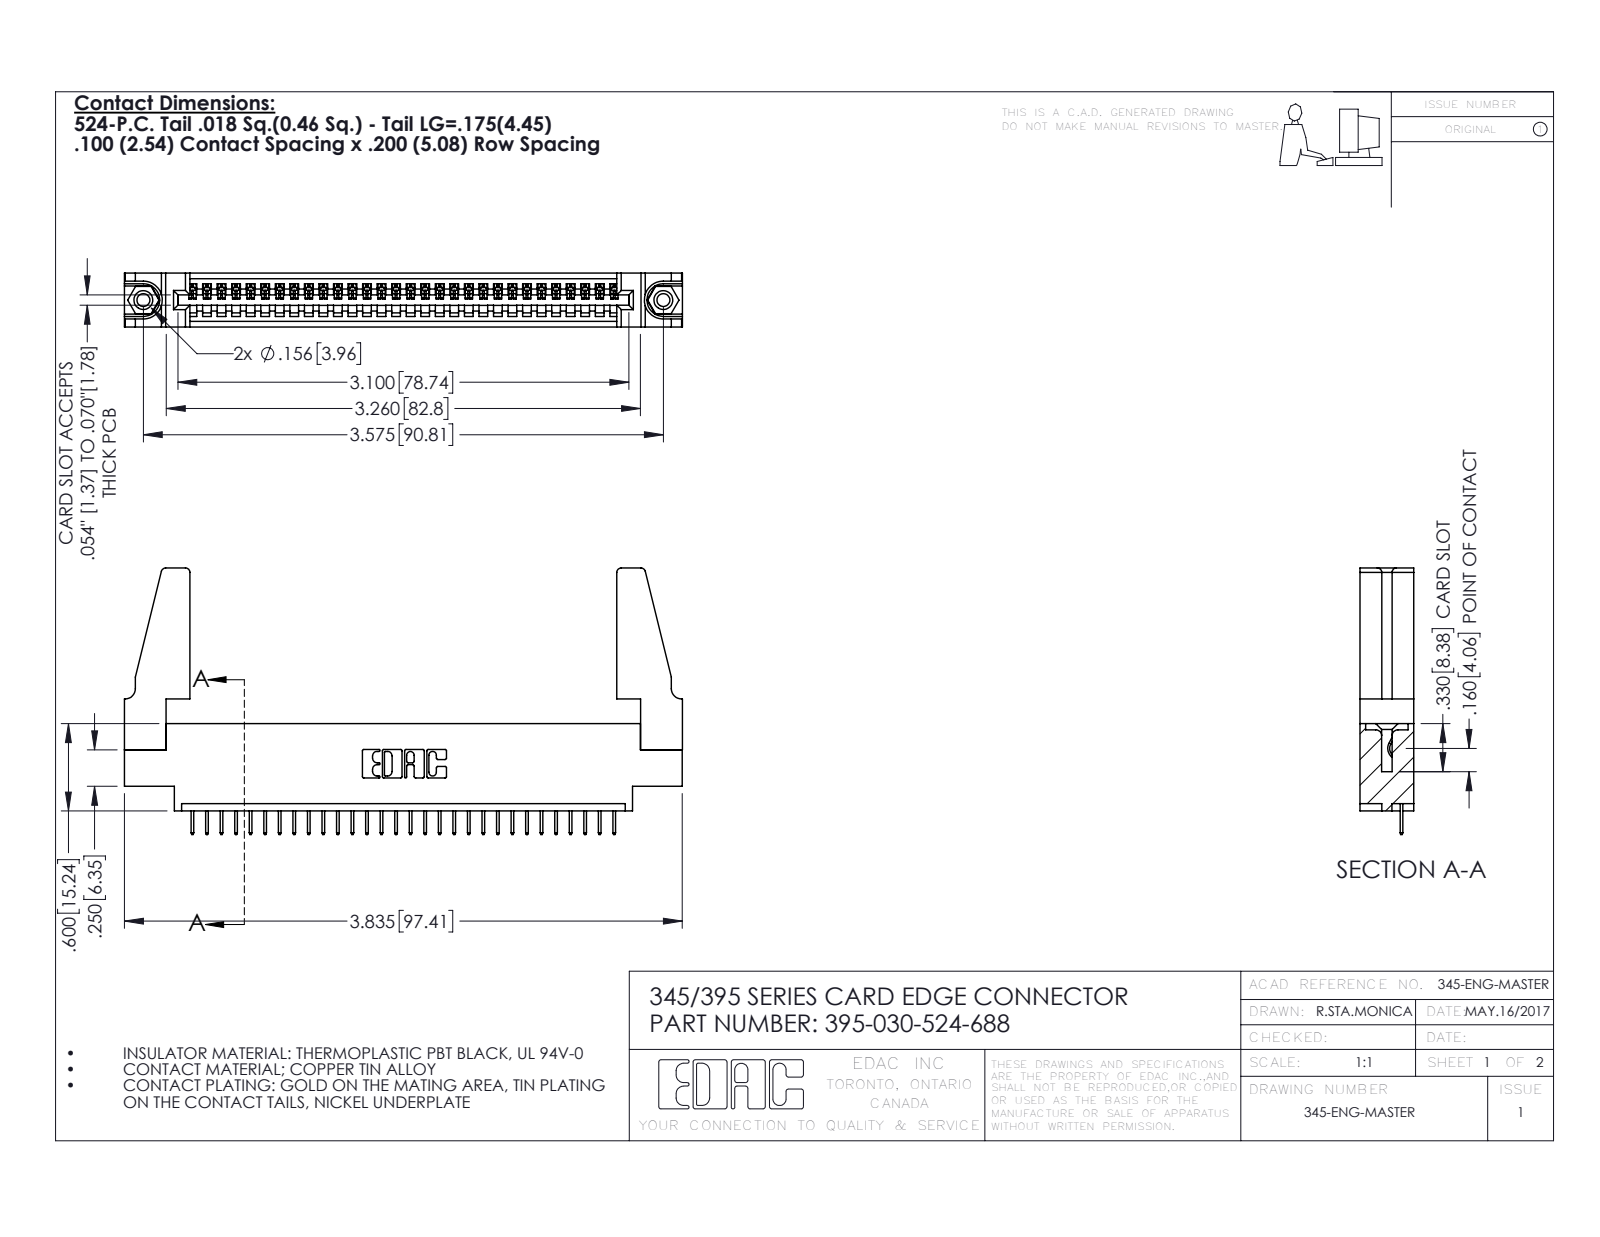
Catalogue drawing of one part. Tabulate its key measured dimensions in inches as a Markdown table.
| quantity | value |
| --- | --- |
| part name | 345-220-078_345-220-088; 345-292-001_345-293-124; 345 Part_0.170 Offset - 0.156 Dia-TH; 345-250-001_345-250-001-102 (+1 more) |
| STEP written by | SolidWorks 2016 (CONFIG_CONTROL_DESIGN) |
| units | inches |
| bodies | 35 solids, 2114 faces (1536 planar, 562 cylindrical, 16 other) |
| overall size | 3.836 × 1.832 × 0.37 |
| volume | 0.743 in³ |
| surface area | 22.59 in² |
| round holes (diameter × count) | 0.089 × 2, 0.125 × 2, 0.156 × 2, 0.064 × 1 |
| round bosses / shafts (diameter × count) | 0.155 × 2 |
| partial cylindrical surfaces (radius × count) | 0.006 × 60, 0.01 × 22, 0.03 × 8, 0.007 × 6, 0.031 × 6, 0.026 × 3, 0.031 × 2, 0.04 × 2 |
| main face-to-face distances | 0.37, 0.072, 0.298, 0.2, 0.098, 0.272, 0.025, 0.225, 0.072, 0.175 |
| hole center spacings | 0.27, 3.34, 3.575 |
